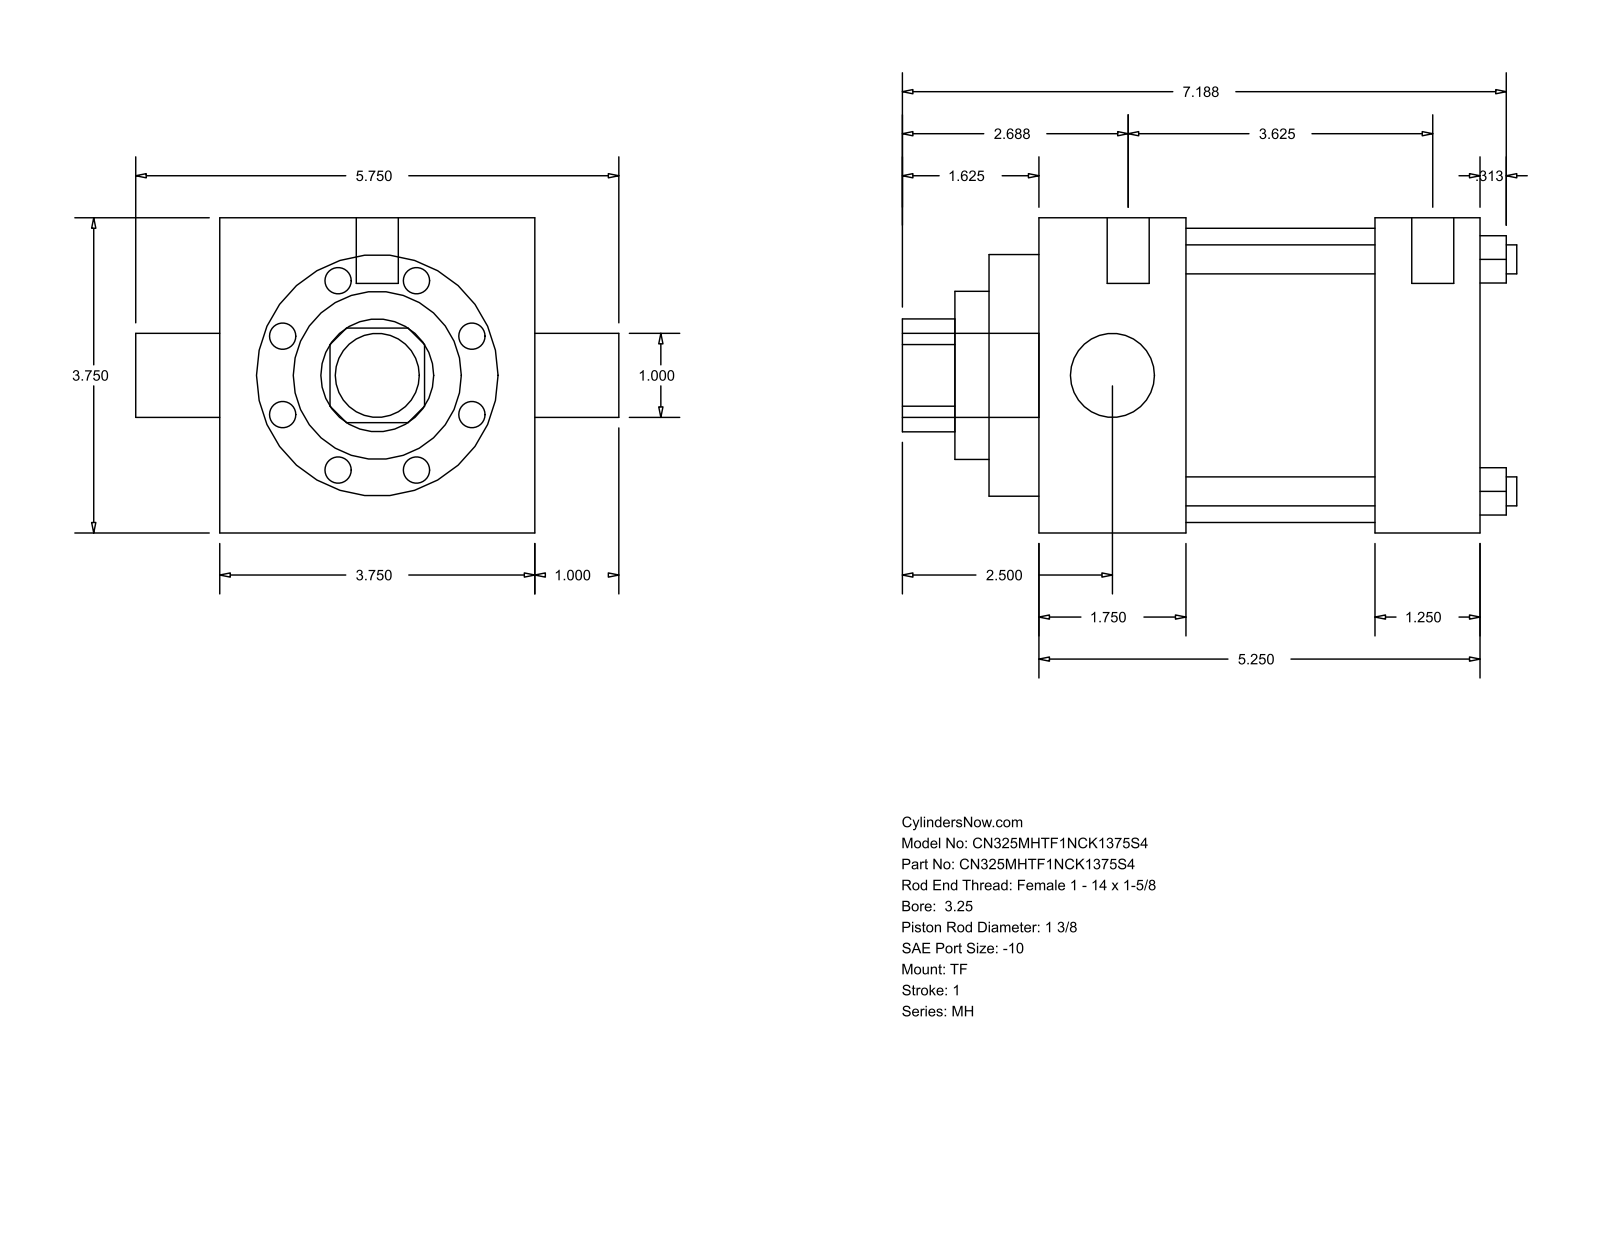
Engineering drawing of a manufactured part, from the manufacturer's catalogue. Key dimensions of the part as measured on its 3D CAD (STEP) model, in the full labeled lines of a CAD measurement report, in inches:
Part name (STEP PRODUCT): MH_TF__0325_1.375
STEP written by: GSSL Pune (CONFIG_CONTROL_DESIGN)
Units: inches
Bodies: 0 solids, 86 faces (61 planar, 25 cylindrical, 0 other)
Overall size (bounding box): 7.313 × 5.75 × 3.75
Round holes (diameter × count): ⌀0.345 ×4, ⌀1 ×1, ⌀1.375 ×1, ⌀2 ×1, ⌀2.875 ×1, ⌀3.5 ×1
Round bosses / shafts (diameter × count): ⌀0.219 ×3, ⌀0.5 ×2, ⌀1 ×1
Partial cylindrical surfaces — rounded edges, fillets, slot ends (radius × count): R0.672 ×1
Main face-to-face distances: 3.75, 5.25, 1.75, 4, 2.25, 3.5, 1.25, 0.594, 2.344, 4.594
Hole centre spacings: 1.952, 2.76, 3.903
